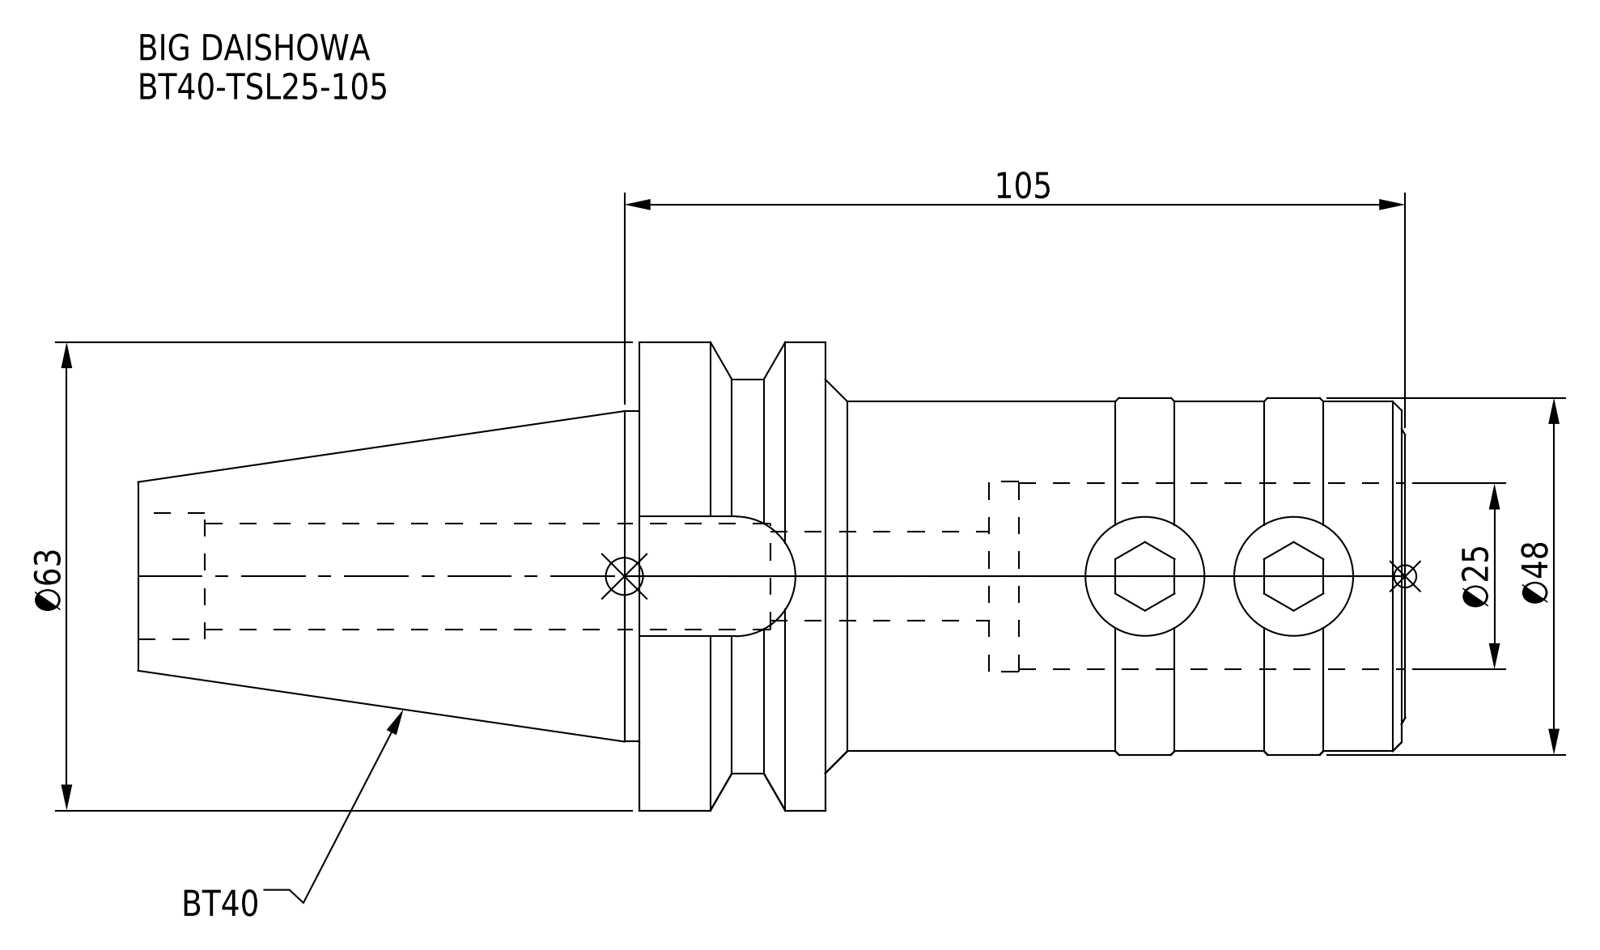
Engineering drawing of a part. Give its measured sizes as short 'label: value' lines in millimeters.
name: BT40-TSL25-105
written by: CREO PARAMETRIC BY PTC INC, 2016380 (AUTOMOTIVE_DESIGN)
unit: mm
bodies: 1 solid, 67 faces (15 planar, 32 cylindrical, 20 other)
size: 170.4 × 63 × 63
volume: 226 068 mm³; area: 39 208 mm²
holes: 1× ⌀12, 1× ⌀14.2, 1× ⌀17, 1× ⌀25, 1× ⌀25.6
bosses: 1× ⌀63, 1× ⌀53, 1× ⌀48, 1× ⌀47, 1× ⌀44.45
rounds: 1× R8.05
face distances: 25, 78, 103, 56, 22, 47, 0.5, 55.5, 77.5, 102.5
